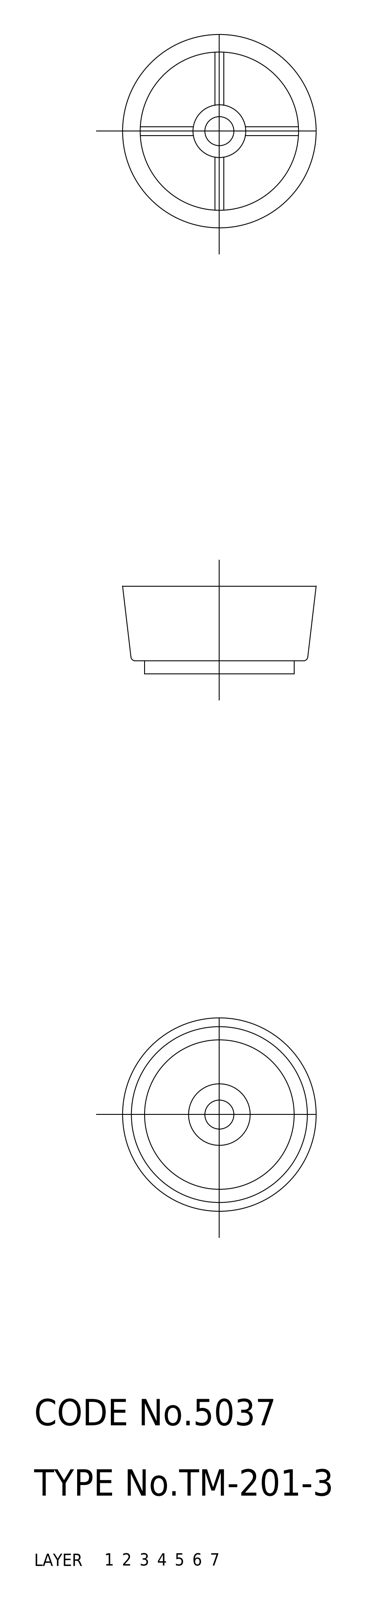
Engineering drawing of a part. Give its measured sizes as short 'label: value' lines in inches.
name: foot; cushion; coat; TM_201_3_32561_36
written by: CADfix (AUTOMOTIVE_DESIGN)
unit: in
bodies: 3 solids, 59 faces (0 planar, 0 cylindrical, 59 other)
size: 0.866 × 0.866 × 0.394
volume: 0.137 in³; area: 4.484 in²
